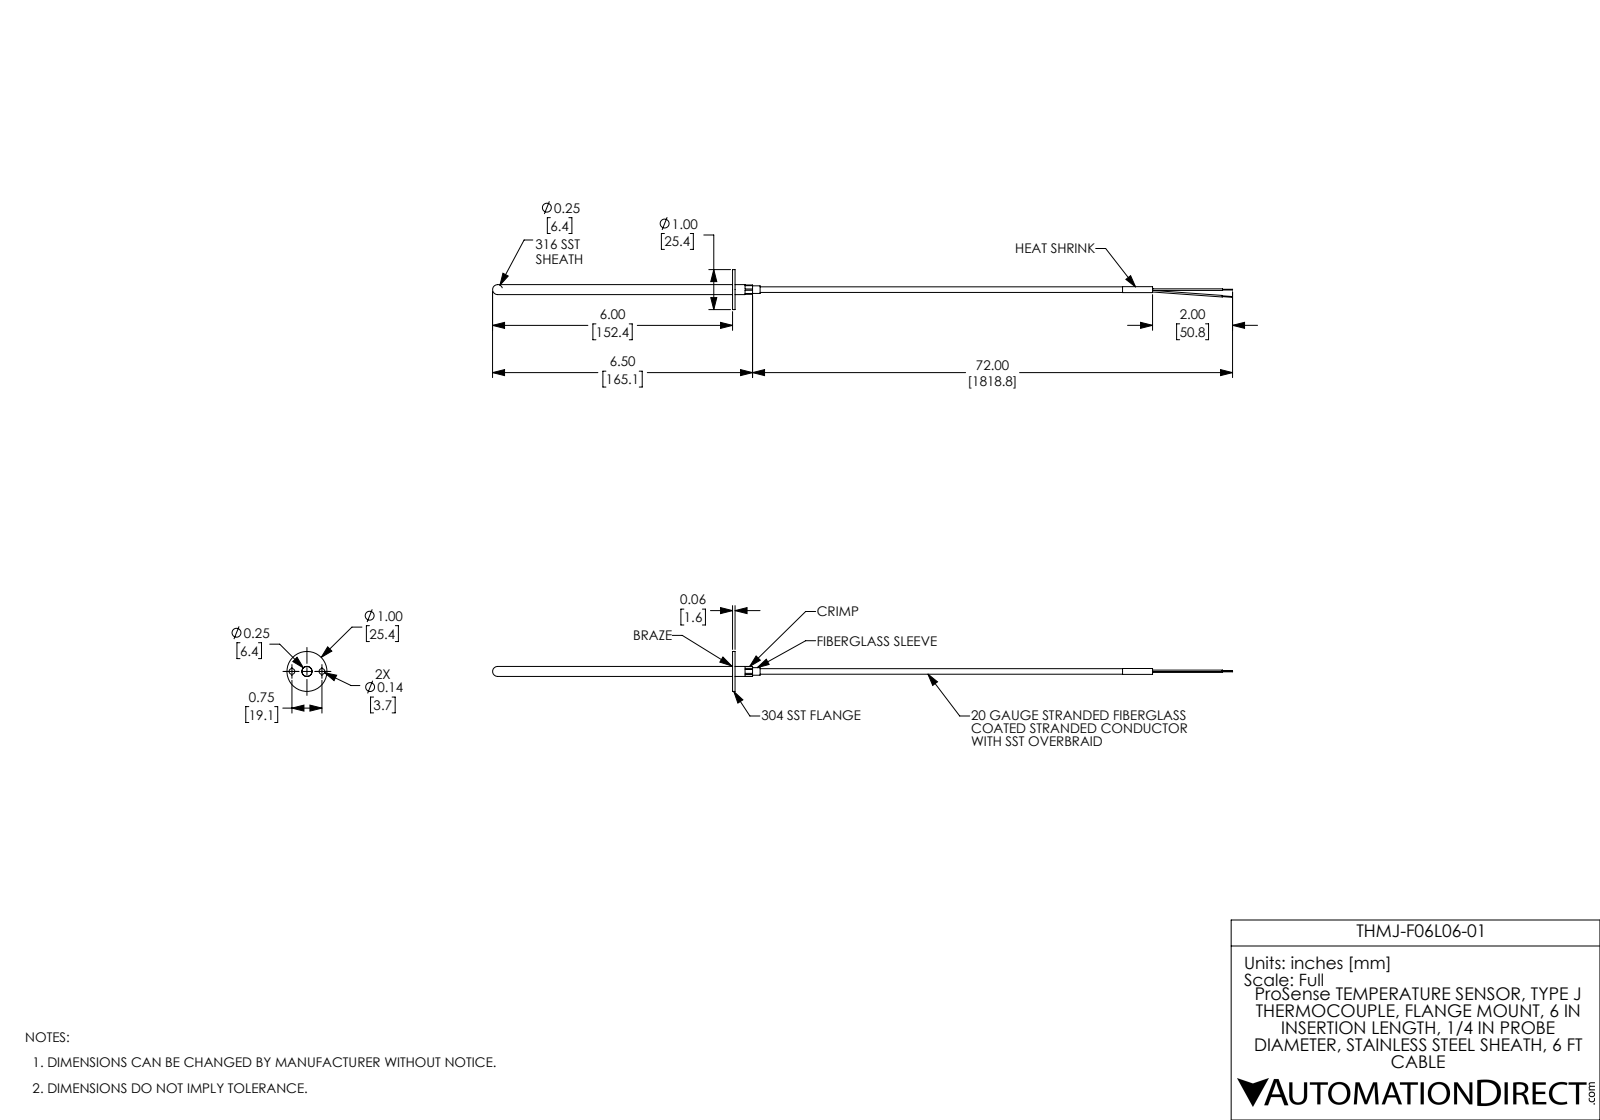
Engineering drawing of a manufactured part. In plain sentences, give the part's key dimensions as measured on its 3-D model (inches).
The part is named "THMJ-F06L06-01". Its 3-D file was written by "SolidWorks 2017 (AUTOMOTIVE_DESIGN)". It is 7 solids with 65 faces: 30 planar, 32 cylindrical and 3 other. Overall it measures 18.5 by 1 by 1 inches. Its volume is 0.532 cubic inches and its surface area 22.25 square inches. Round holes: 3 of diameter 0.144, 1 of diameter 0.136, 1 of diameter 0.189, 1 of diameter 0.257. Round bosses or shafts: 1 of diameter 1, 1 of diameter 0.25, 1 of diameter 0.19, 1 of diameter 0.188, 1 of diameter 0.148, 1 of diameter 0.14, 1 of diameter 0.132, 1 of diameter 0.04. The main face-to-face distances are 0.063, 0.5, 0.437, 0.231, 0.188, 0.75, 0.062, 0.124, 0.562, 0.688. The hole center spacings are 0.375, 0.375, 0.75.
